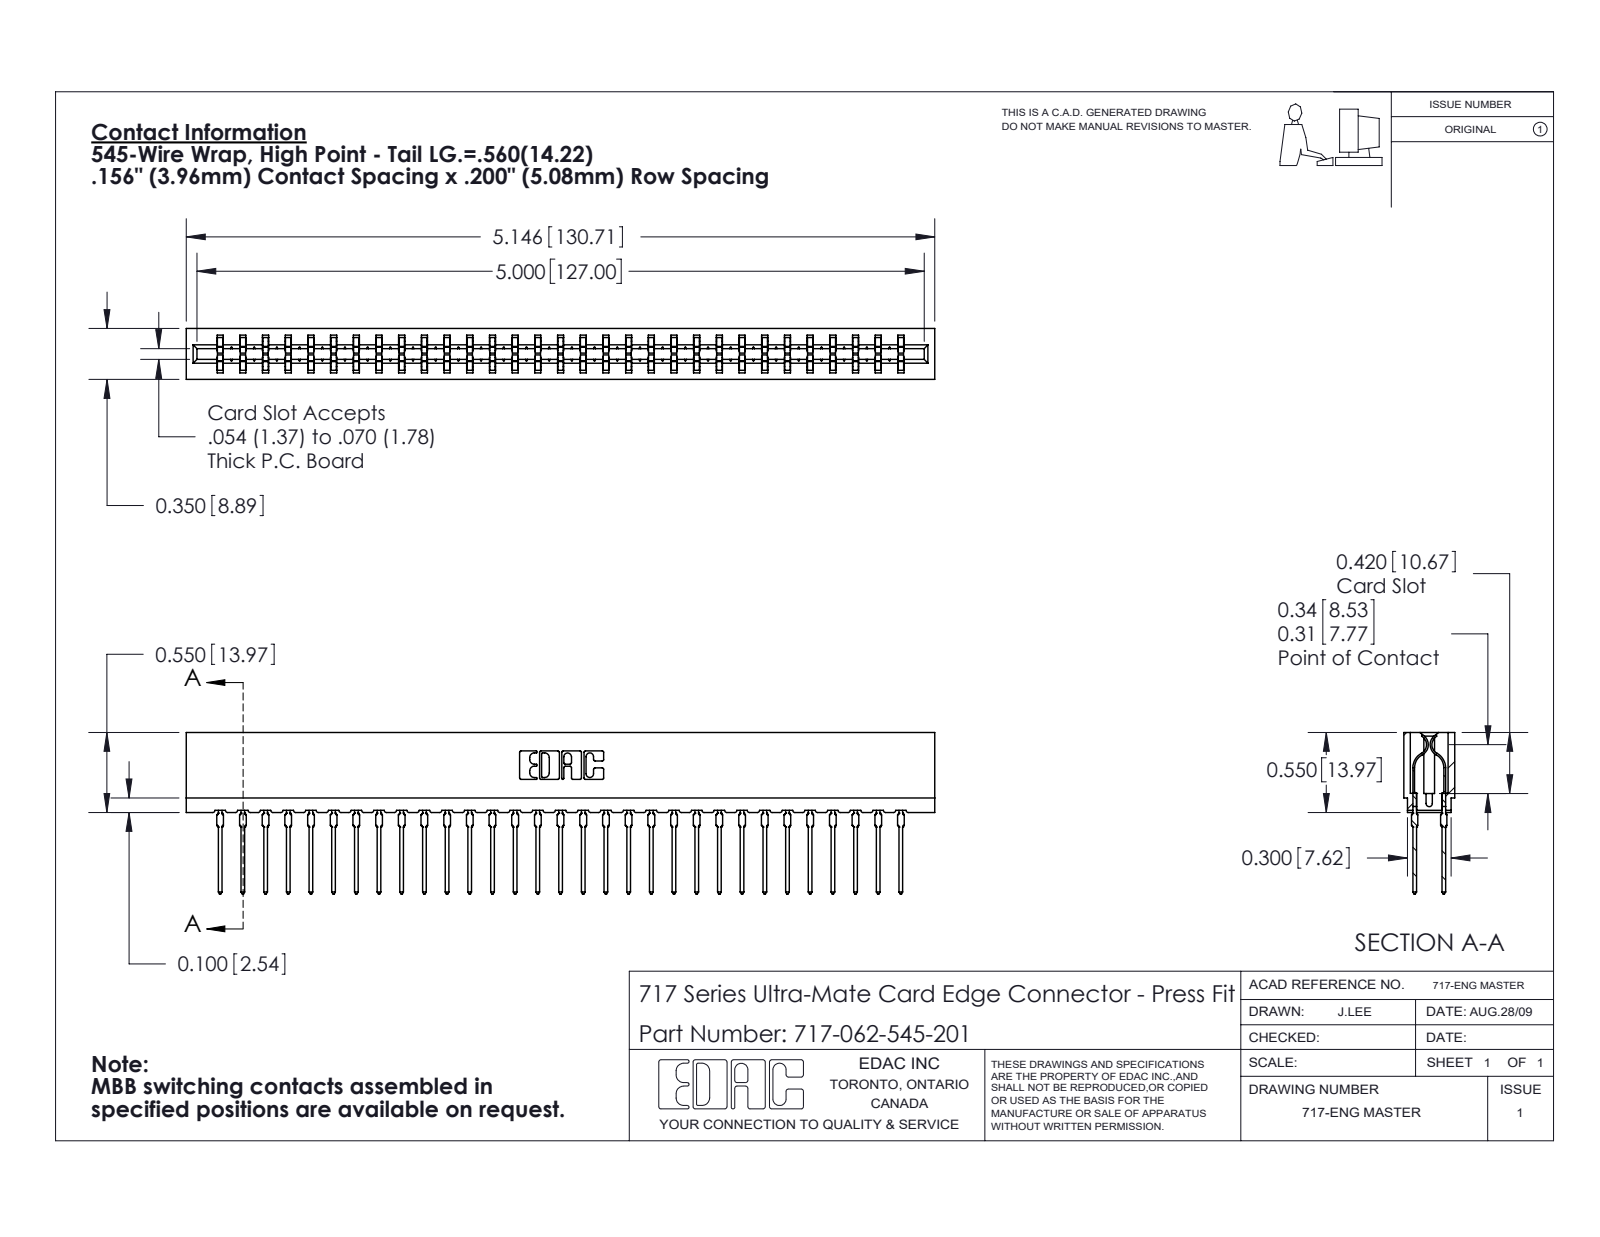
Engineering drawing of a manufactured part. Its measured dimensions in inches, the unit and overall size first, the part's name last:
Units: inches
Overall size (bounding box): 5.146 × 1.109 × 0.35
Partial cylindrical surfaces — rounded edges, fillets, slot ends (radius × count): R0.021 ×124, R0.015 ×62, R0.01 ×22, R0.005 ×8, R0.011 ×8, R0.007 ×6, R0.031 ×6, R0.026 ×3
Main face-to-face distances: 0.212, 0.138, 0.35, 0.063, 0.287, 0.076, 0.149, 0.074, 0.087, 0.263
Volume: 0.707 in³ · Surface area: 28.88 in²
Bodies: 63 solids, 5674 faces (2937 planar, 1125 cylindrical, 1612 other)
Part name (STEP PRODUCT): 717-062-545-201; 717 Part_Insulator Option - 06; 745-292-001_545
STEP written by: SolidWorks 2020 (CONFIG_CONTROL_DESIGN)
